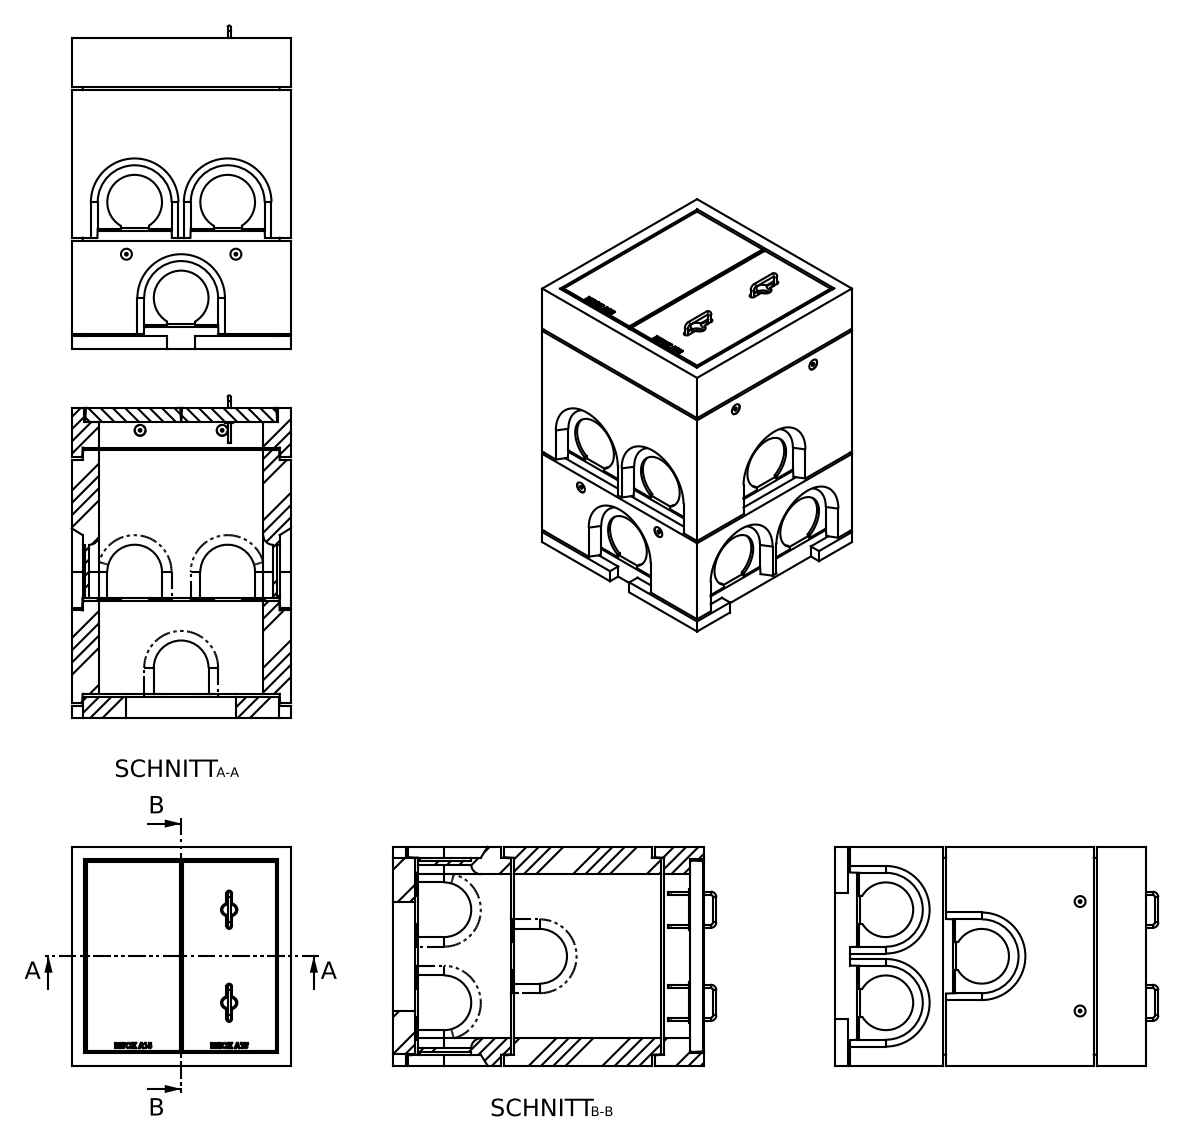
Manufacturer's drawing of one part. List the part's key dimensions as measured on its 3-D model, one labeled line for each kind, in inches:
Part name (STEP PRODUCT): SC-A15.0606.15.107
STEP written by: SolidWorks 2018 (AUTOMOTIVE_DESIGN)
Units: inches
Bodies: 0 solids, 425 faces (289 planar, 62 cylindrical, 74 other)
Overall size (bounding box): 46.483 × 31.496 × 31.496
Round holes (diameter × count): ⌀7.874 ×6, ⌀0.787 ×4, ⌀1.575 ×4
Round bosses / shafts (diameter × count): ⌀0.472 ×5, ⌀0.229 ×4, ⌀0.394 ×2
Partial cylindrical surfaces — rounded edges, fillets, slot ends (radius × count): R1.378 ×16, R0.394 ×1
Main face-to-face distances: 31.496, 27.559, 3.937, 1.969, 0.394, 23.622, 1.378, 44.685, 13.78, 29.528
Hole centre spacings: 13.386, 15.319, 4.724, 7.573, 10.083, 15.748, 16.214, 16.375
